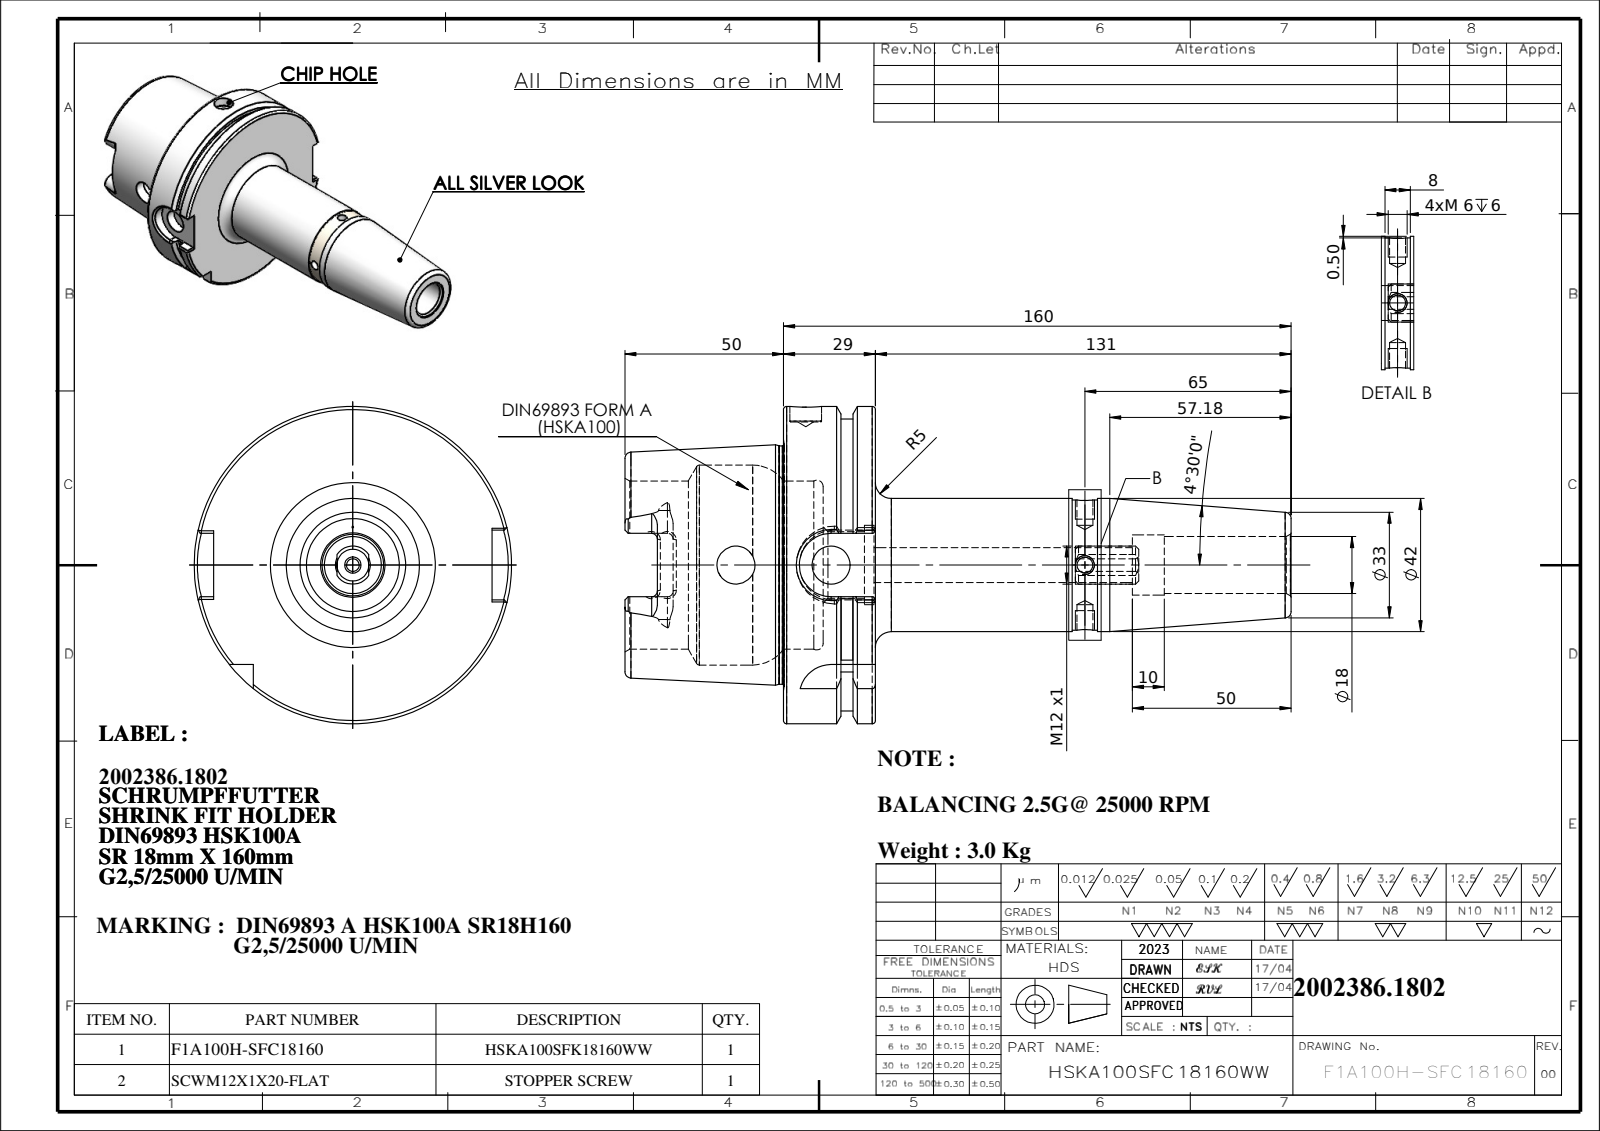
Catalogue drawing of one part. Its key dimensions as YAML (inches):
part_name: "SCWM12X1X20-FLAT; HSKA100SFC18160WW; 91100A-SR18160"
step_written_by: "SolidWorks 2018 (CONFIG_CONTROL_DESIGN)"
units: inches
bodies: {solids: 2, faces: 216, planar: 59, cylindrical: 69, other: 88}
overall_size: [8.268, 3.937, 3.937]
volume: 24.41
surface_area: 112.8
round_holes:
  - {diameter: 0.197, count: 2}
  - {diameter: 0.472, count: 2}
  - {diameter: 0.157, count: 1}
  - {diameter: 0.394, count: 1}
  - {diameter: 0.433, count: 1}
  - {diameter: 0.708, count: 1}
  - {diameter: 0.748, count: 1}
  - {diameter: 0.827, count: 1}
  - {diameter: 0.984, count: 1}
  - {diameter: 2.087, count: 1}
  - {diameter: 2.48, count: 1}
round_bosses_or_shafts:
  - {diameter: 3.937, count: 1}
  - {diameter: 3.622, count: 1}
  - {diameter: 2.959, count: 1}
  - {diameter: 1.654, count: 1}
  - {diameter: 1.614, count: 1}
partial_cylinders:
  - {radius: 0.071, count: 6}
  - {radius: 0.192, count: 4}
  - {radius: 0.394, count: 2}
  - {radius: 0.236, count: 1}
  - {radius: 0.433, count: 1}
face_to_face_distances: [1.14, 0.492, 0.648, 1.969, 2.461, 3.108, 6.299, 3.091, 2.83, 0.861]
hole_center_spacings: [1.181, 3.15, 3.465, 4.331]
